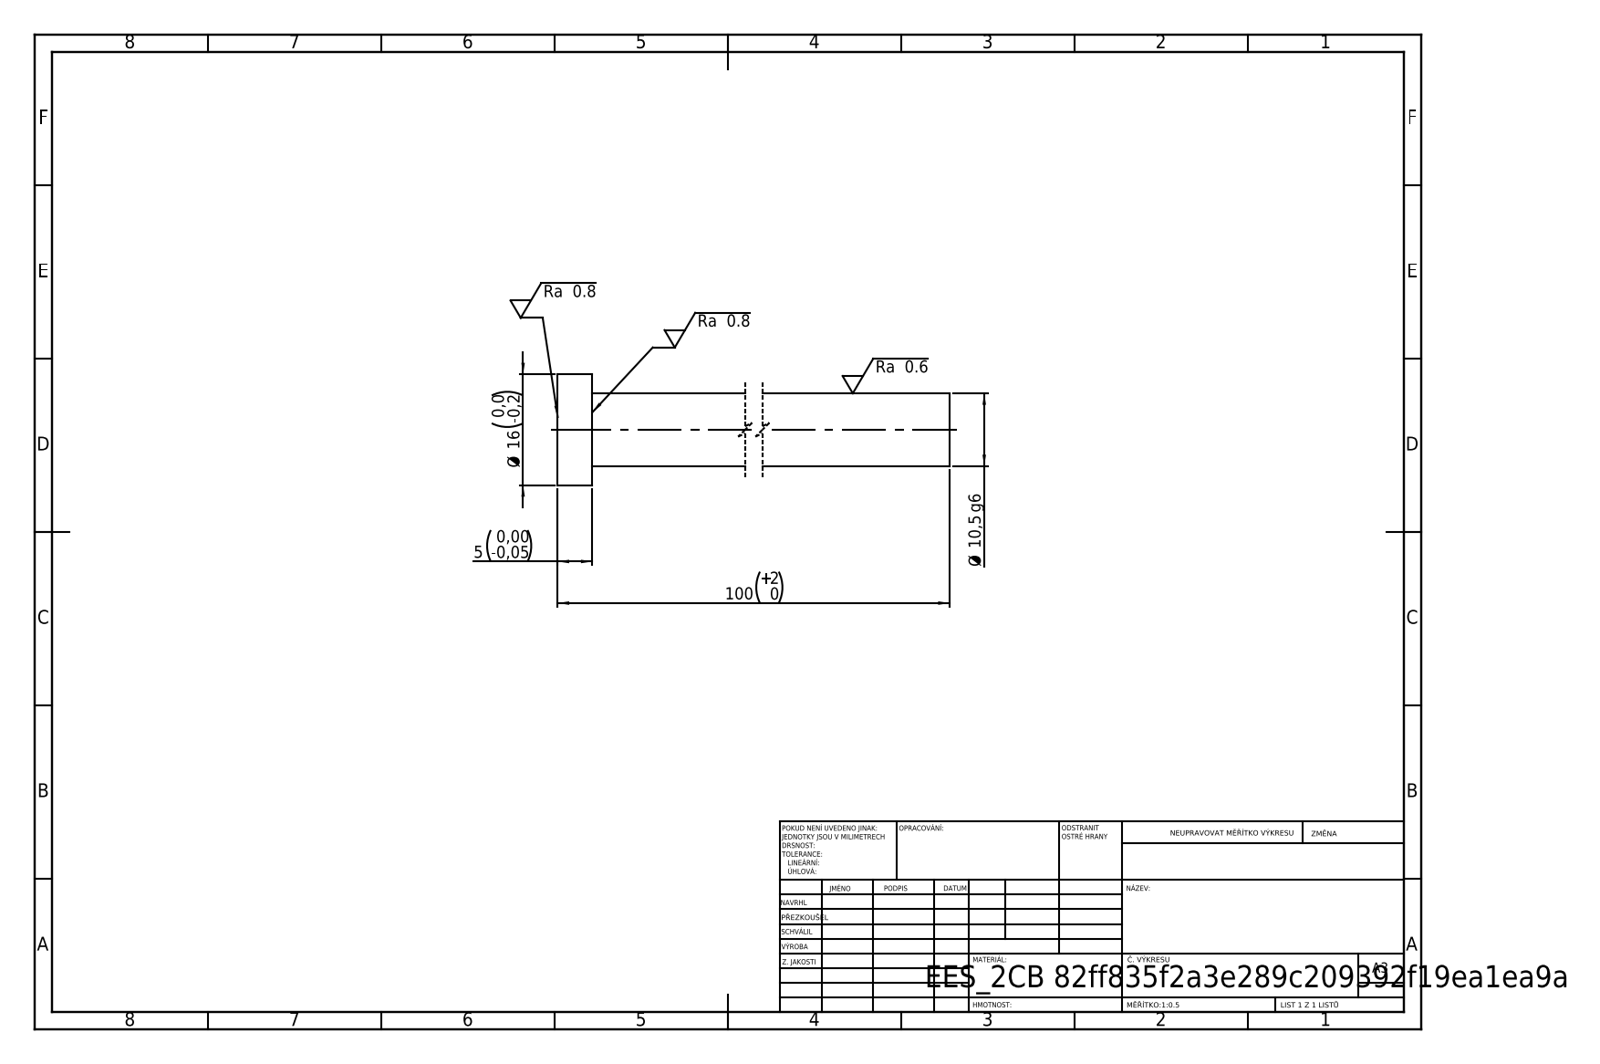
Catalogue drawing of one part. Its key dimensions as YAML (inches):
step_written_by: "SolidWorks 2019 (CONFIG_CONTROL_DESIGN)"
units: inches
bodies: {solids: 1, faces: 7, planar: 3, cylindrical: 4, other: 0}
overall_size: [3.937, 0.63, 0.63]
volume: 0.563
surface_area: 5.87
round_bosses_or_shafts:
  - {diameter: 0.63, count: 1}
  - {diameter: 0.413, count: 1}
face_to_face_distances: [0.197, 3.937, 3.74]
